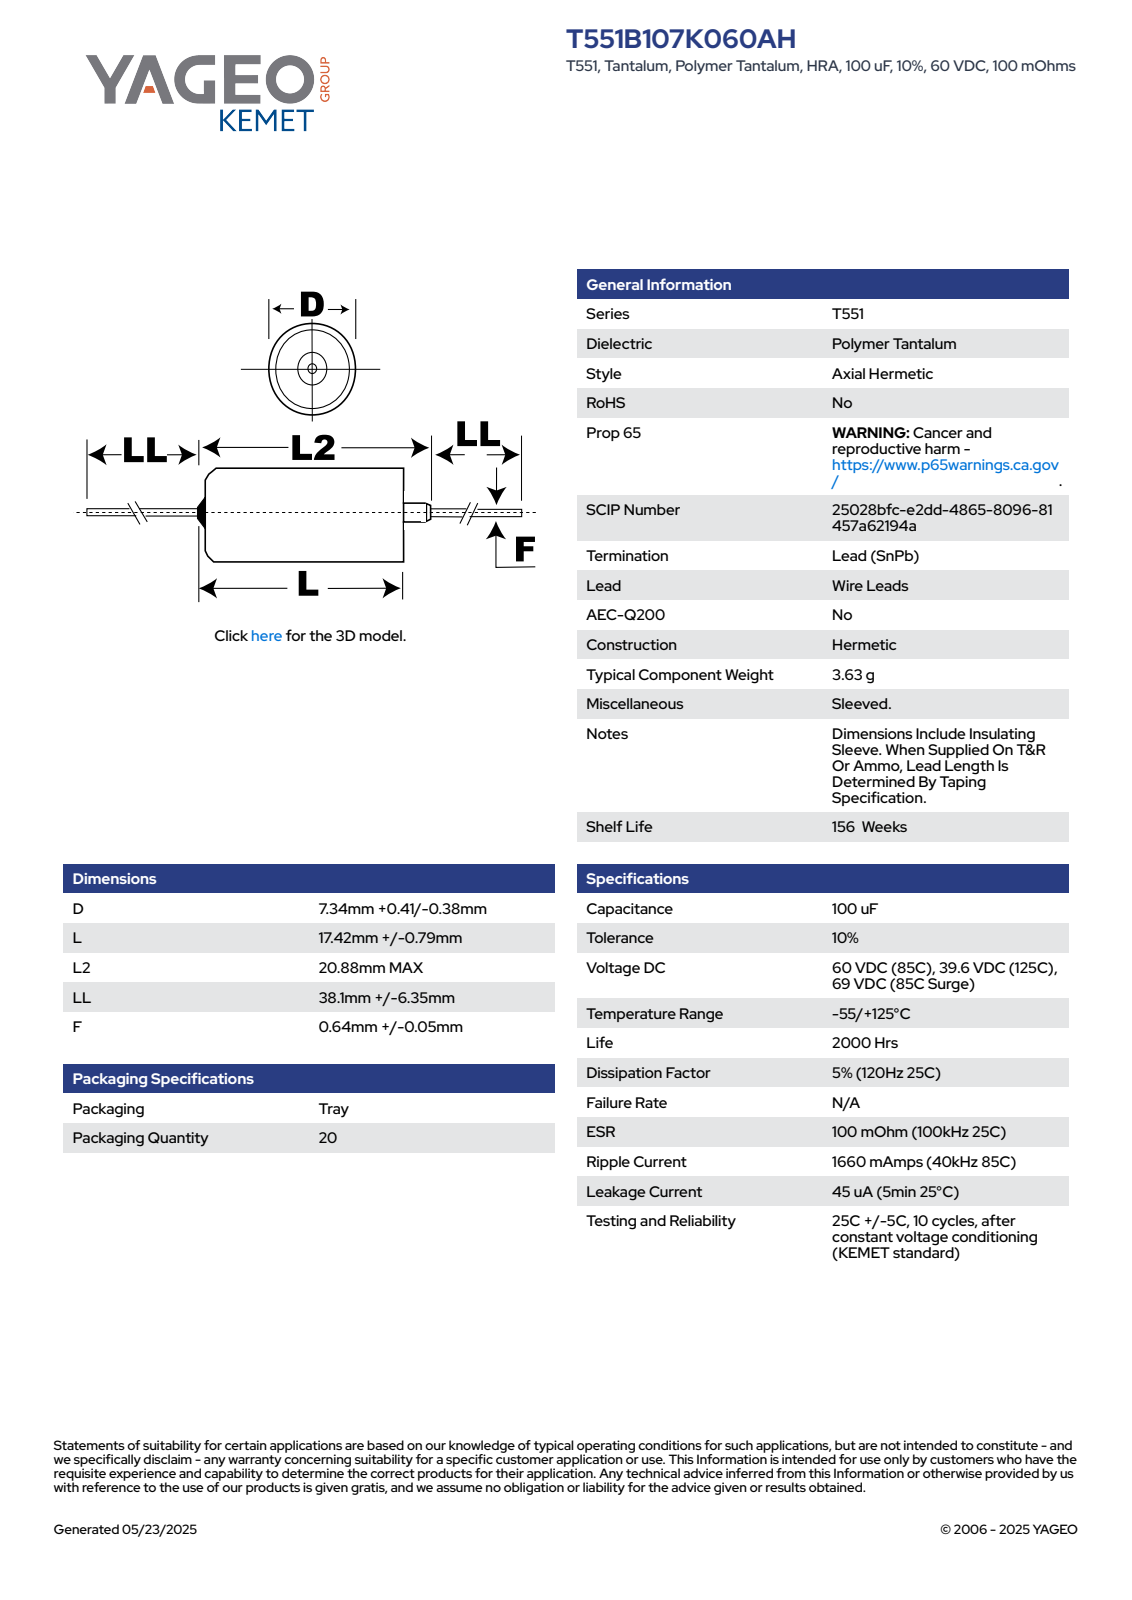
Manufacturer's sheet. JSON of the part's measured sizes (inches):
{"part_name": "CTAM_NOG_B_D7.75L18.21L220.88LL44.45F0.69", "step_written_by": "SolidWorks 2014 (AUTOMOTIVE_DESIGN)", "units": "inches", "bodies": {"solids": 1, "faces": 98, "planar": 29, "cylindrical": 30, "other": 39}, "overall_size": [4.217, 0.305, 0.305], "volume_in3": 0.043, "surface_area_in2": 1.32, "round_holes": [[0.289, 1]], "round_bosses_or_shafts": [[0.305, 1], [0.052, 1], [0.051, 1], [0.027, 1]], "partial_cylinders_radius": [[0.152, 1]], "face_to_face_distances": [0.532, 0.71, 0.178, 1.757, 2.289, 2.467, 4.217, 2.46, 1.928, 1.75]}
